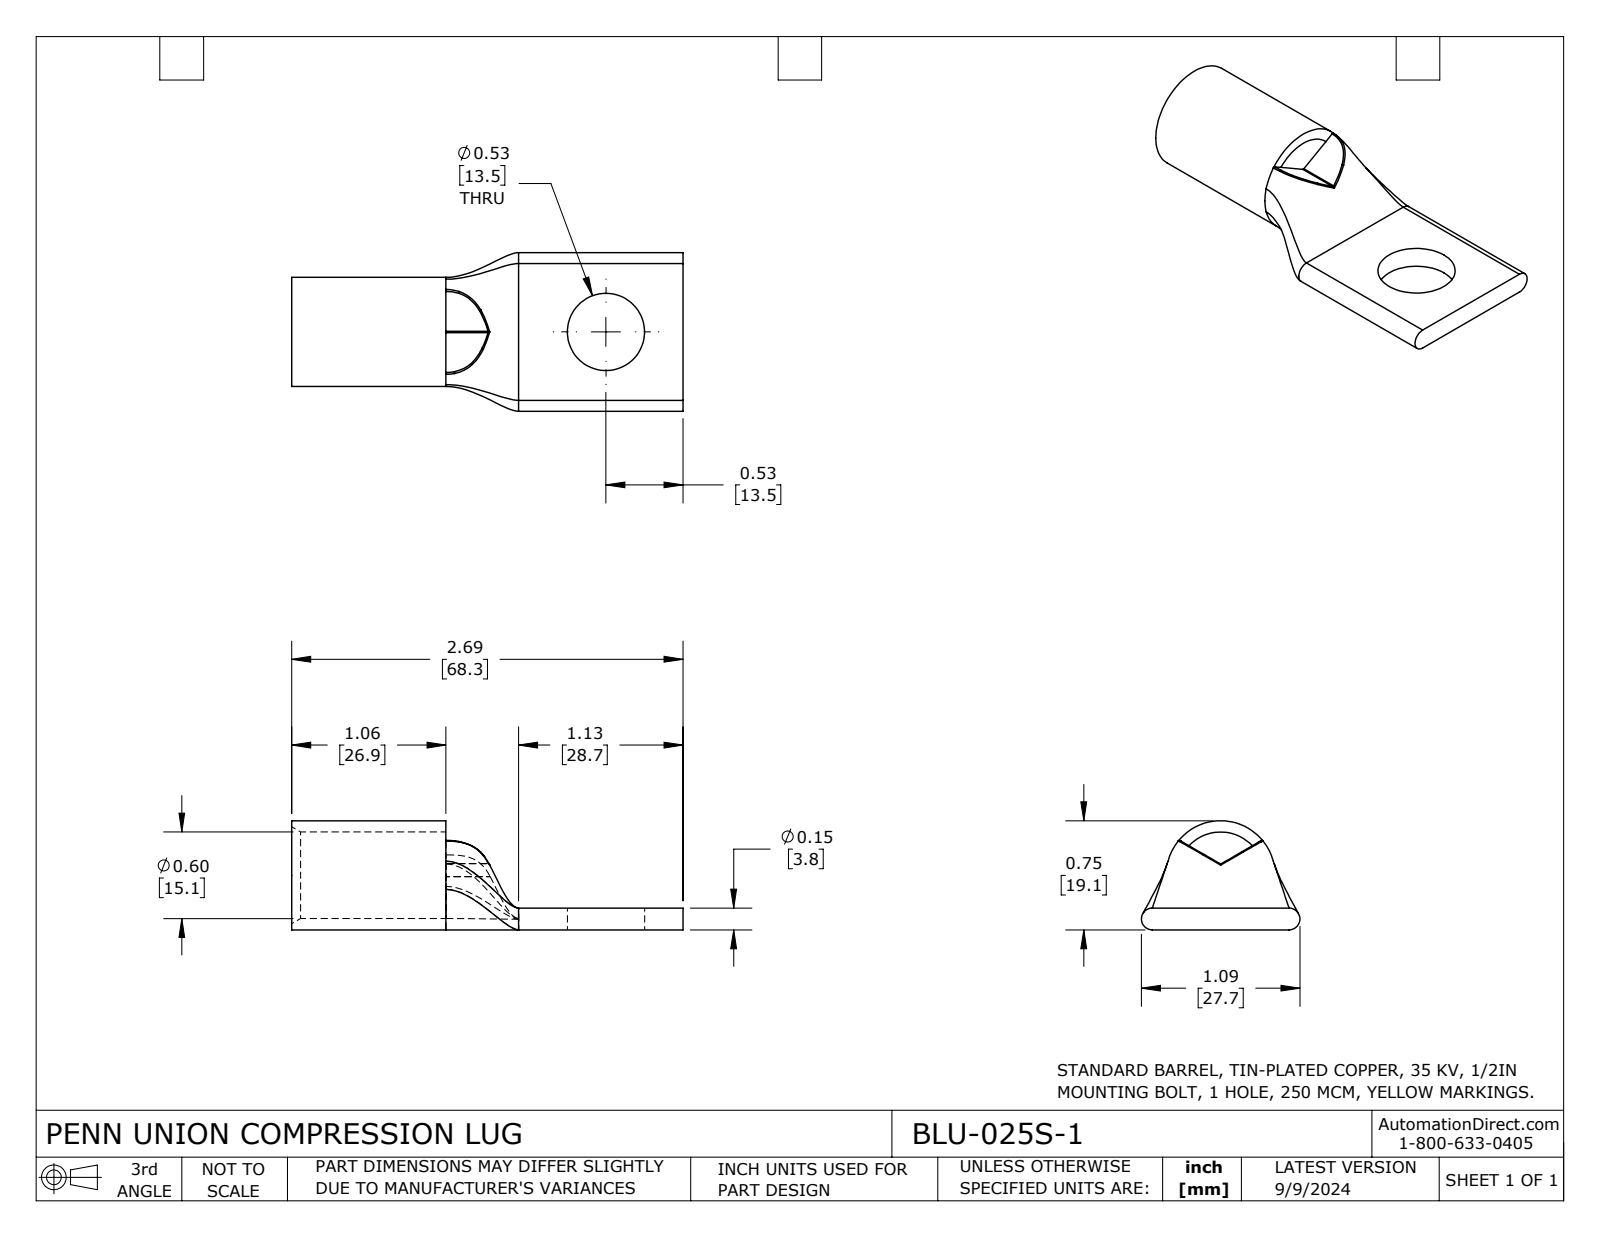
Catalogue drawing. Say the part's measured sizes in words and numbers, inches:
The part is named "BLU-025S-1". Its 3-D file was written by "SolidWorks 2023 (CONFIG_CONTROL_DESIGN)". It is 1 solid with 39 faces: 11 planar, 11 cylindrical and 17 other. Overall it measures 2.69 by 1.09 by 0.75 inches. Its volume is 0.393 cubic inches and its surface area 9.715 square inches. Round holes: 1 of diameter 0.531, 1 of diameter 0.595. Round bosses or shafts: 1 of diameter 0.75. Partial cylindrical surfaces (rounded edges, fillets, slot ends): 2 of radius 0.01, 2 of radius 0.075. The main face-to-face distances are 0.15, 0.078, 2.69, 1.06, 1.63, 1.56, 0.5, 1.13.
